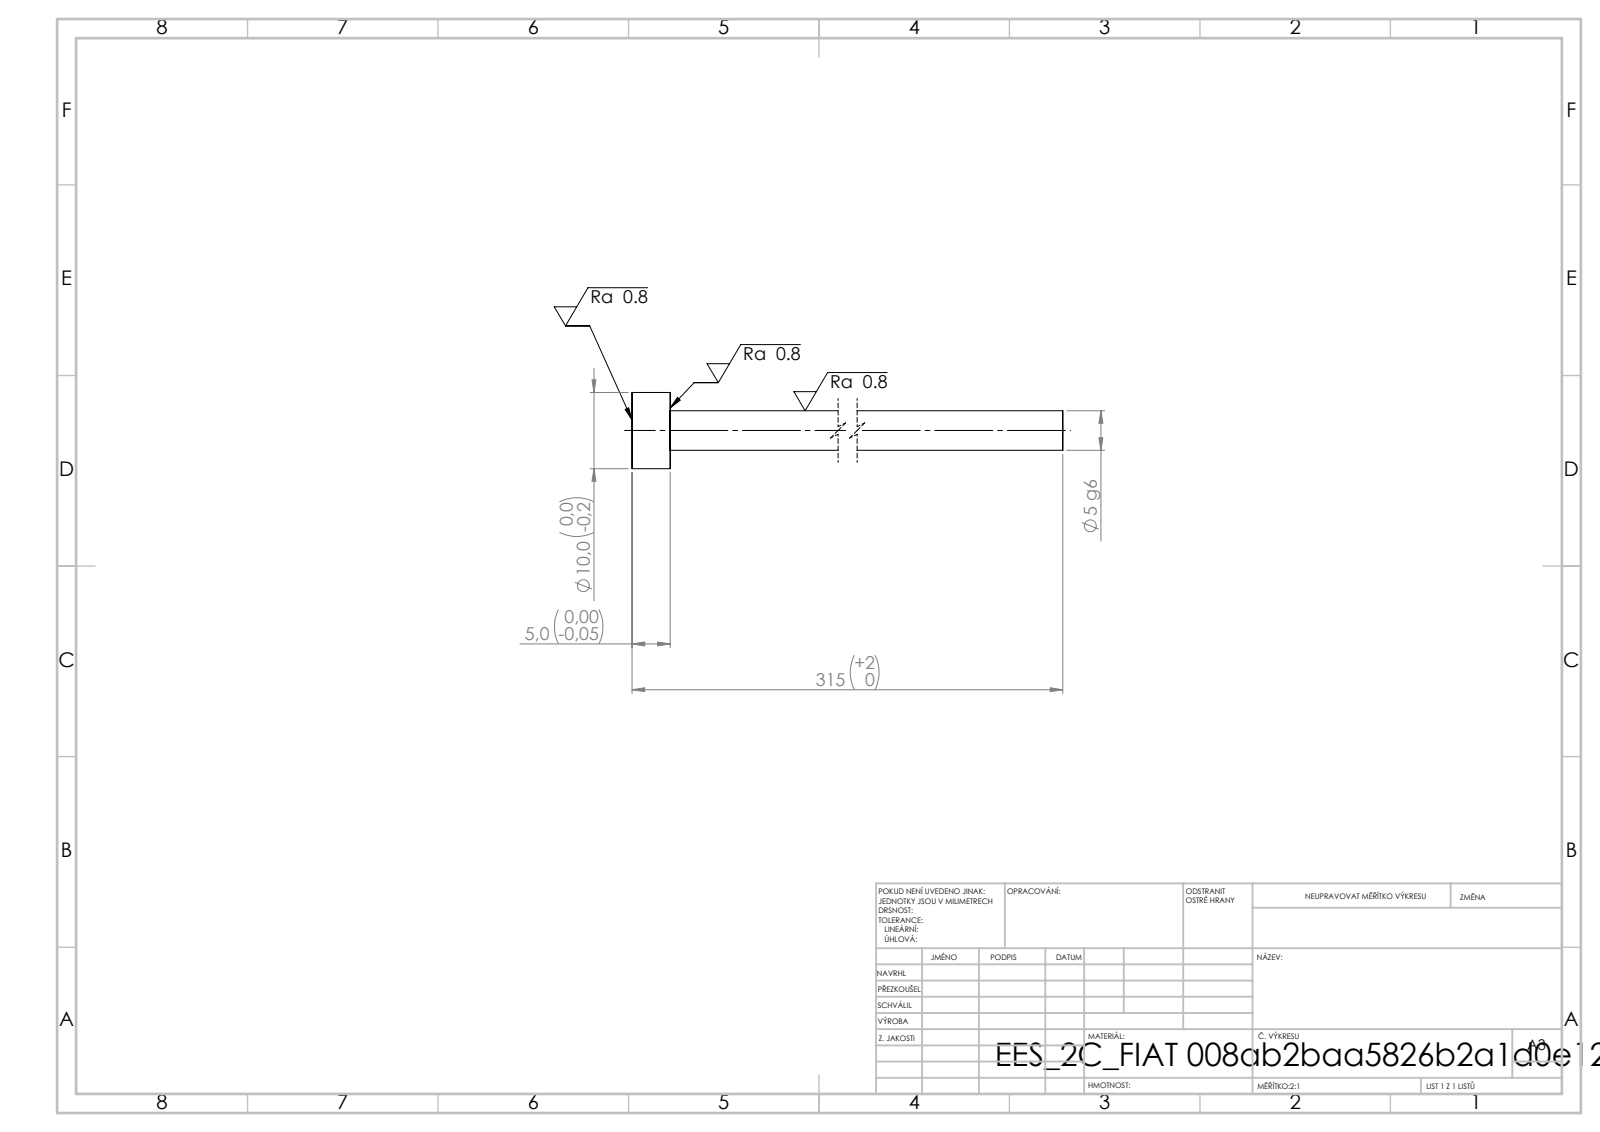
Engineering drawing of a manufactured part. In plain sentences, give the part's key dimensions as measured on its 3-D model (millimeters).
Its 3-D file was written by "SolidWorks 2019 (CONFIG_CONTROL_DESIGN)". It is 1 solid with 7 faces: 3 planar, 4 cylindrical and 0 other. Overall it measures 315 by 10 by 10 millimeters. Its volume is 6 976 cubic millimeters and its surface area 5 378 square millimeters. Round bosses or shafts: 1 of diameter 10, 1 of diameter 5.2. The main face-to-face distances are 5, 315, 310.
